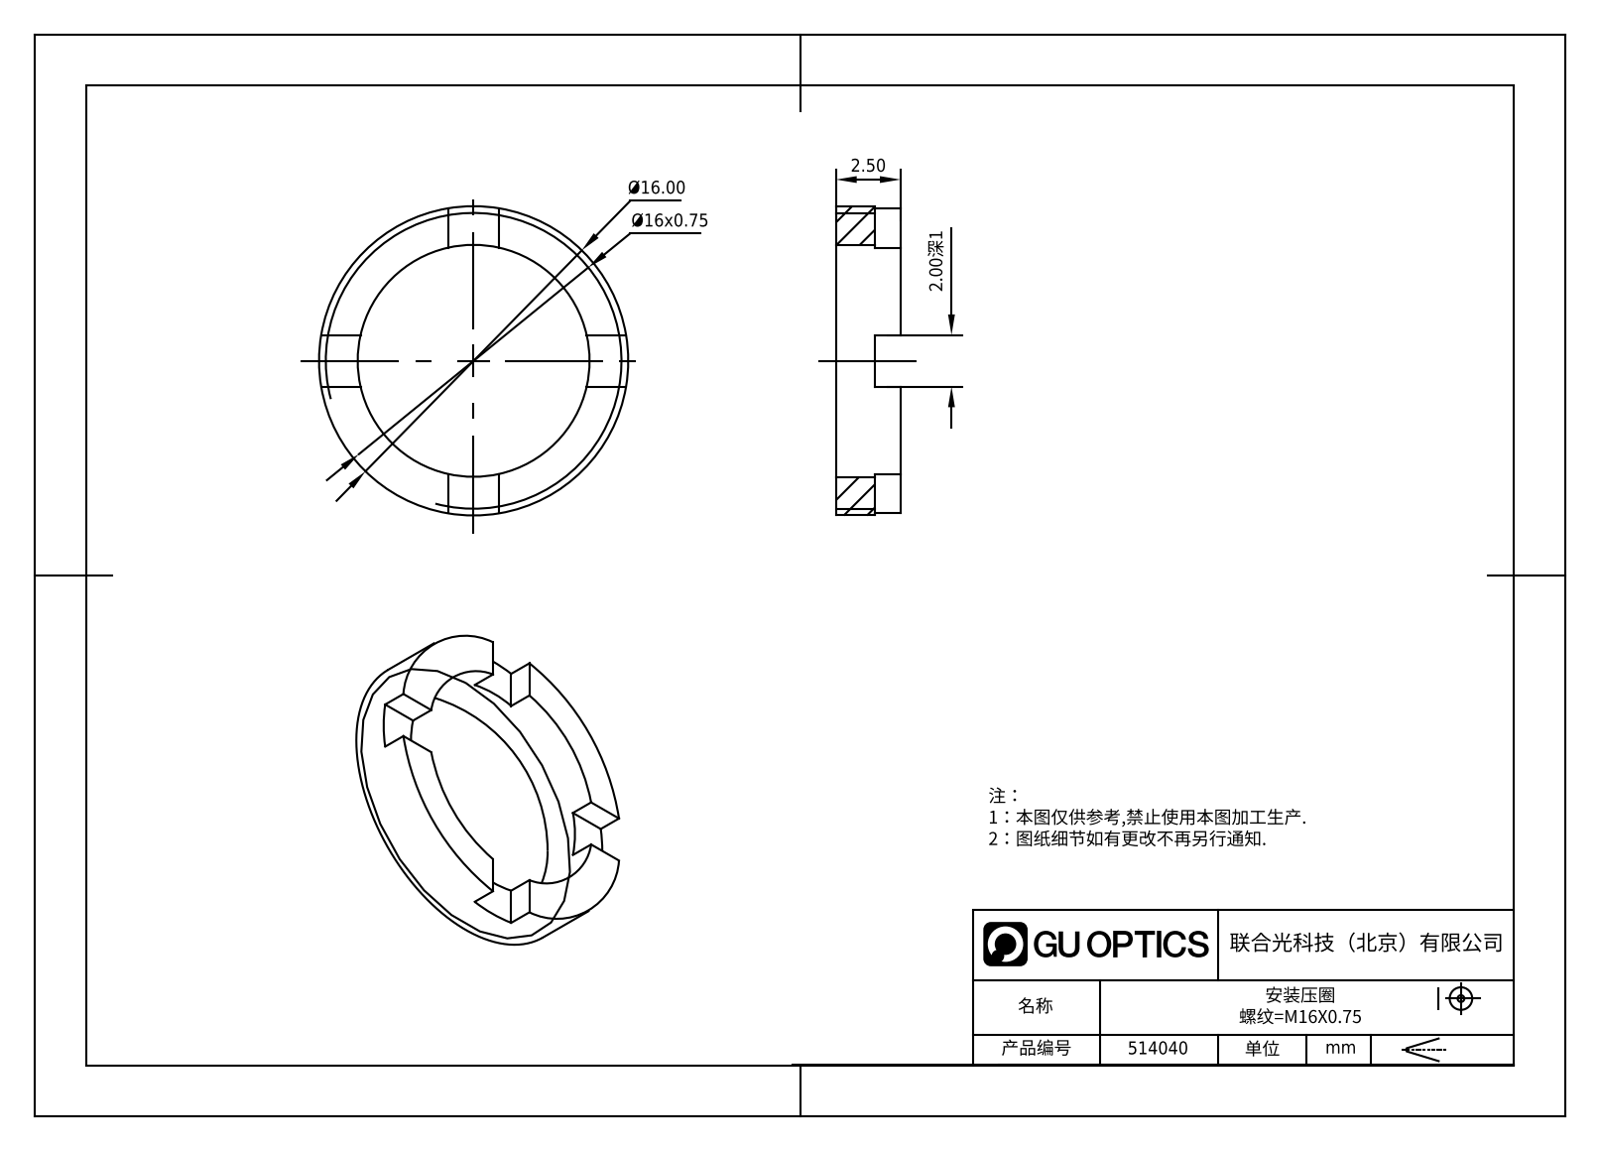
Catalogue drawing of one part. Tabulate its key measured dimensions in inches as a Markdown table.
| quantity | value |
| --- | --- |
| part name | 514040 |
| STEP written by | SolidWorks 2020 (CONFIG_CONTROL_DESIGN) |
| units | inches |
| bodies | 1 solid, 21 faces (17 planar, 4 cylindrical, 0 other) |
| overall size | 0.63 × 0.63 × 0.098 |
| volume | 0.01 in³ |
| surface area | 0.558 in² |
| round holes (diameter × count) | 0.512 × 1 |
| round bosses / shafts (diameter × count) | 0.63 × 1 |
| main face-to-face distances | 0.098, 0.059, 0.039, 0.079 |
